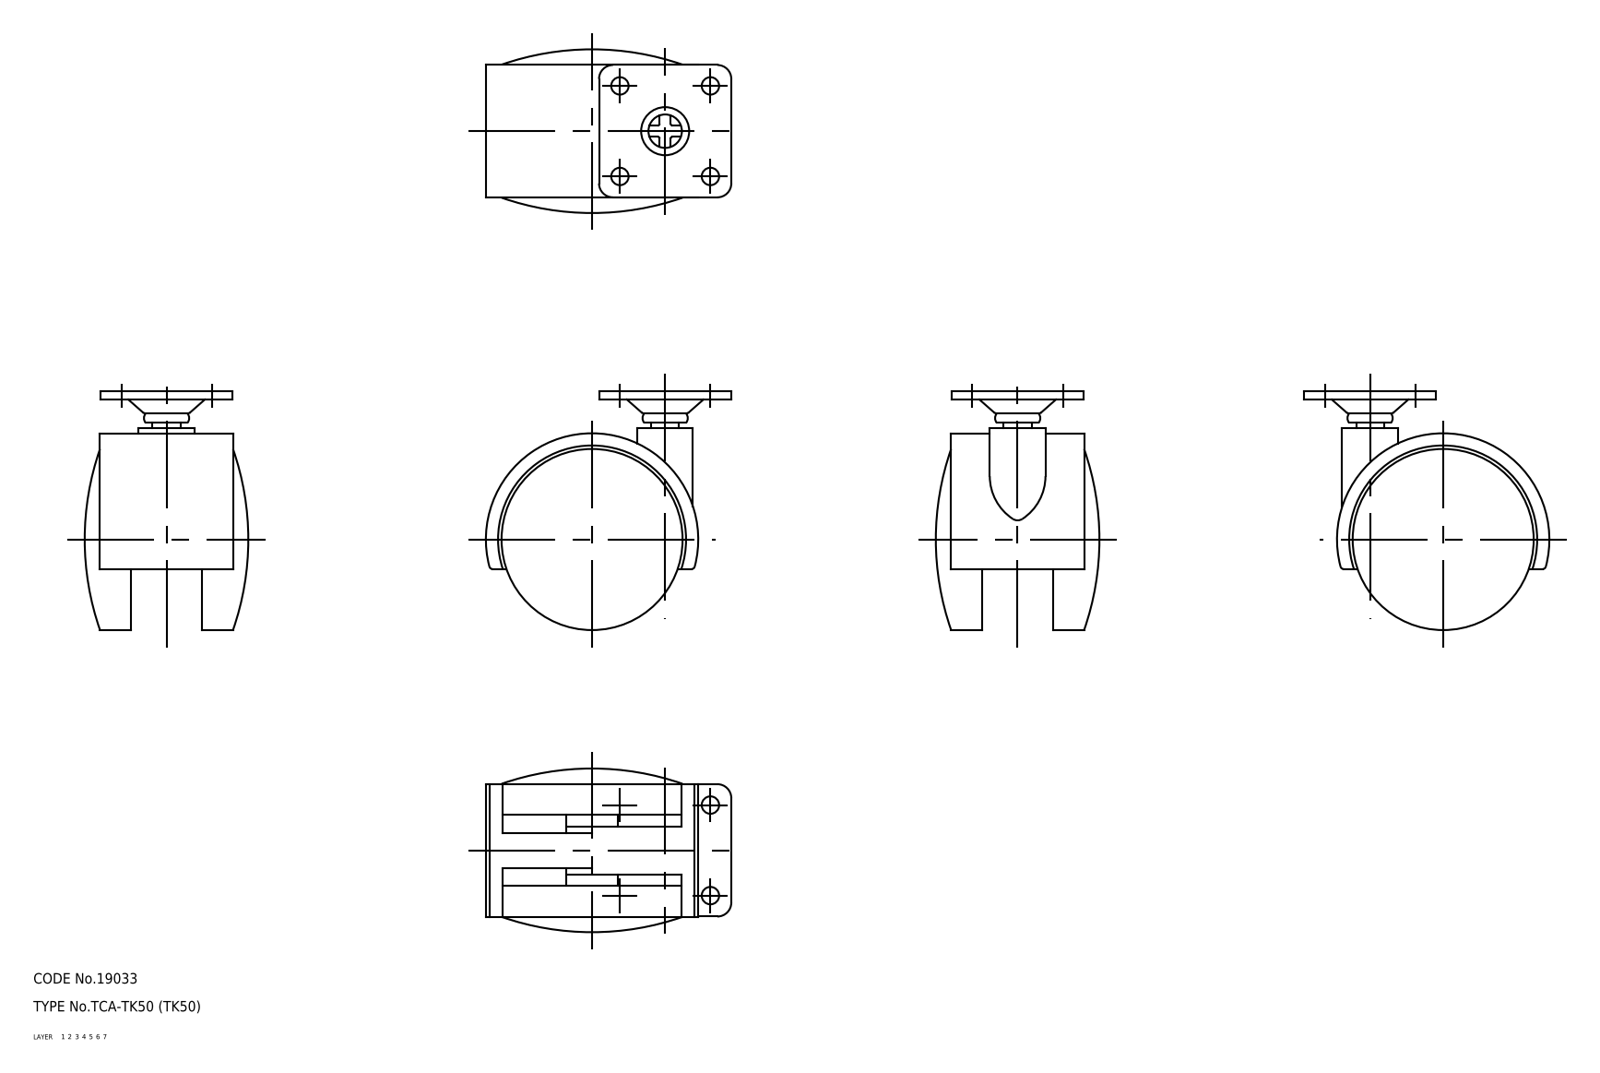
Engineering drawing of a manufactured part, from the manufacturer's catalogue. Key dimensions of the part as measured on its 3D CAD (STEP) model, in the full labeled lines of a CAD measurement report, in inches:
Part name (STEP PRODUCT): wheel; mounting plate; main shaft; TK50_4398_36
STEP written by: CADfix (AUTOMOTIVE_DESIGN)
Units: inches
Bodies: 5 solids, 118 faces (0 planar, 0 cylindrical, 118 other)
Overall size (bounding box): 2.815 × 2.697 × 1.85
Volume: 4.419 in³ · Surface area: 50.89 in²
